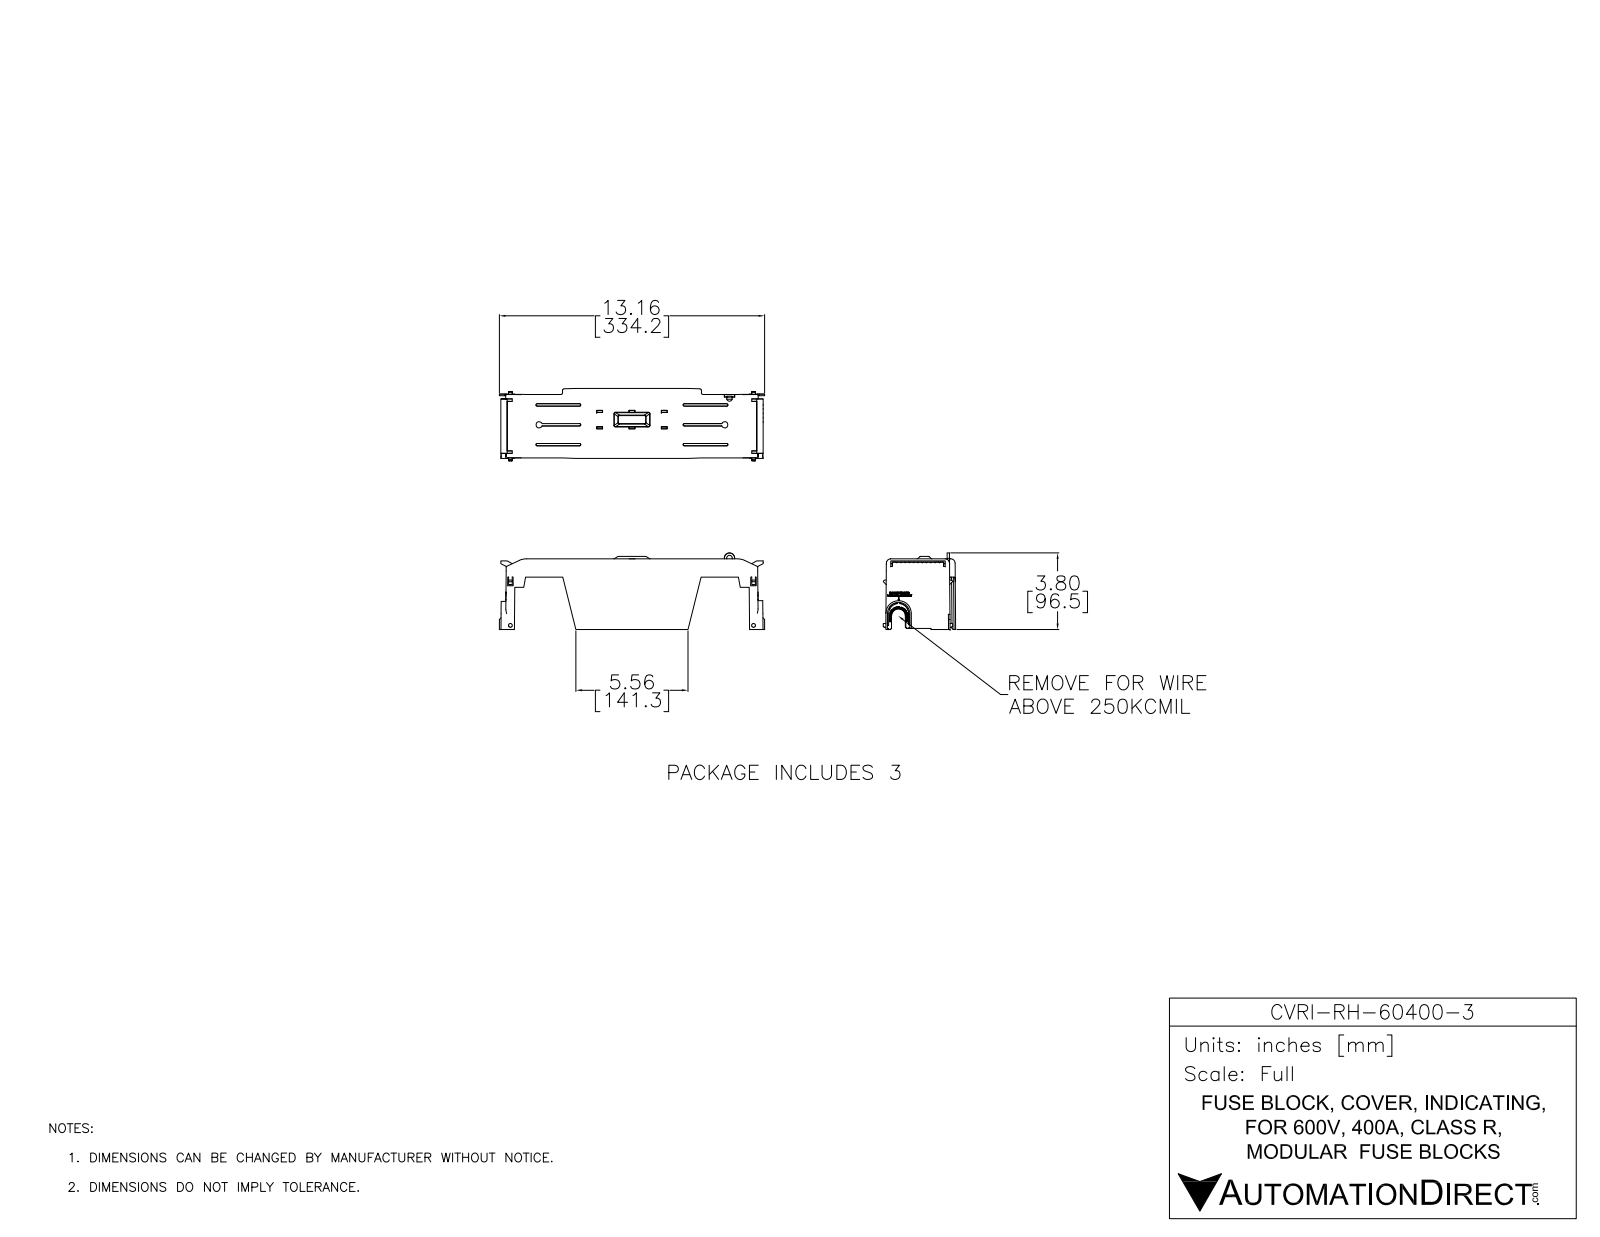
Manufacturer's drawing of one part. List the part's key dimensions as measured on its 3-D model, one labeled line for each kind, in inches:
Part name (STEP PRODUCT): CVRI-RH-60400-3
STEP written by: SolidWorks 2017 (AUTOMOTIVE_DESIGN)
Units: inches
Bodies: 1 solid, 2374 faces (1611 planar, 104 cylindrical, 659 other)
Overall size (bounding box): 13.158 × 3.8 × 3.594
Volume: 10.25 in³ · Surface area: 270.7 in²
Round holes (diameter × count): ⌀0.276 ×1
Partial cylindrical surfaces — rounded edges, fillets, slot ends (radius × count): R0.039 ×18, R0.079 ×8, R0.118 ×8, R0.138 ×8, R0.217 ×8, R0.01 ×2, R0.02 ×2, R0.04 ×2
Main face-to-face distances: 0.079, 0.276, 0.197, 0.354, 0.118, 0.803, 1.472, 0.669, 0.236, 4.974
